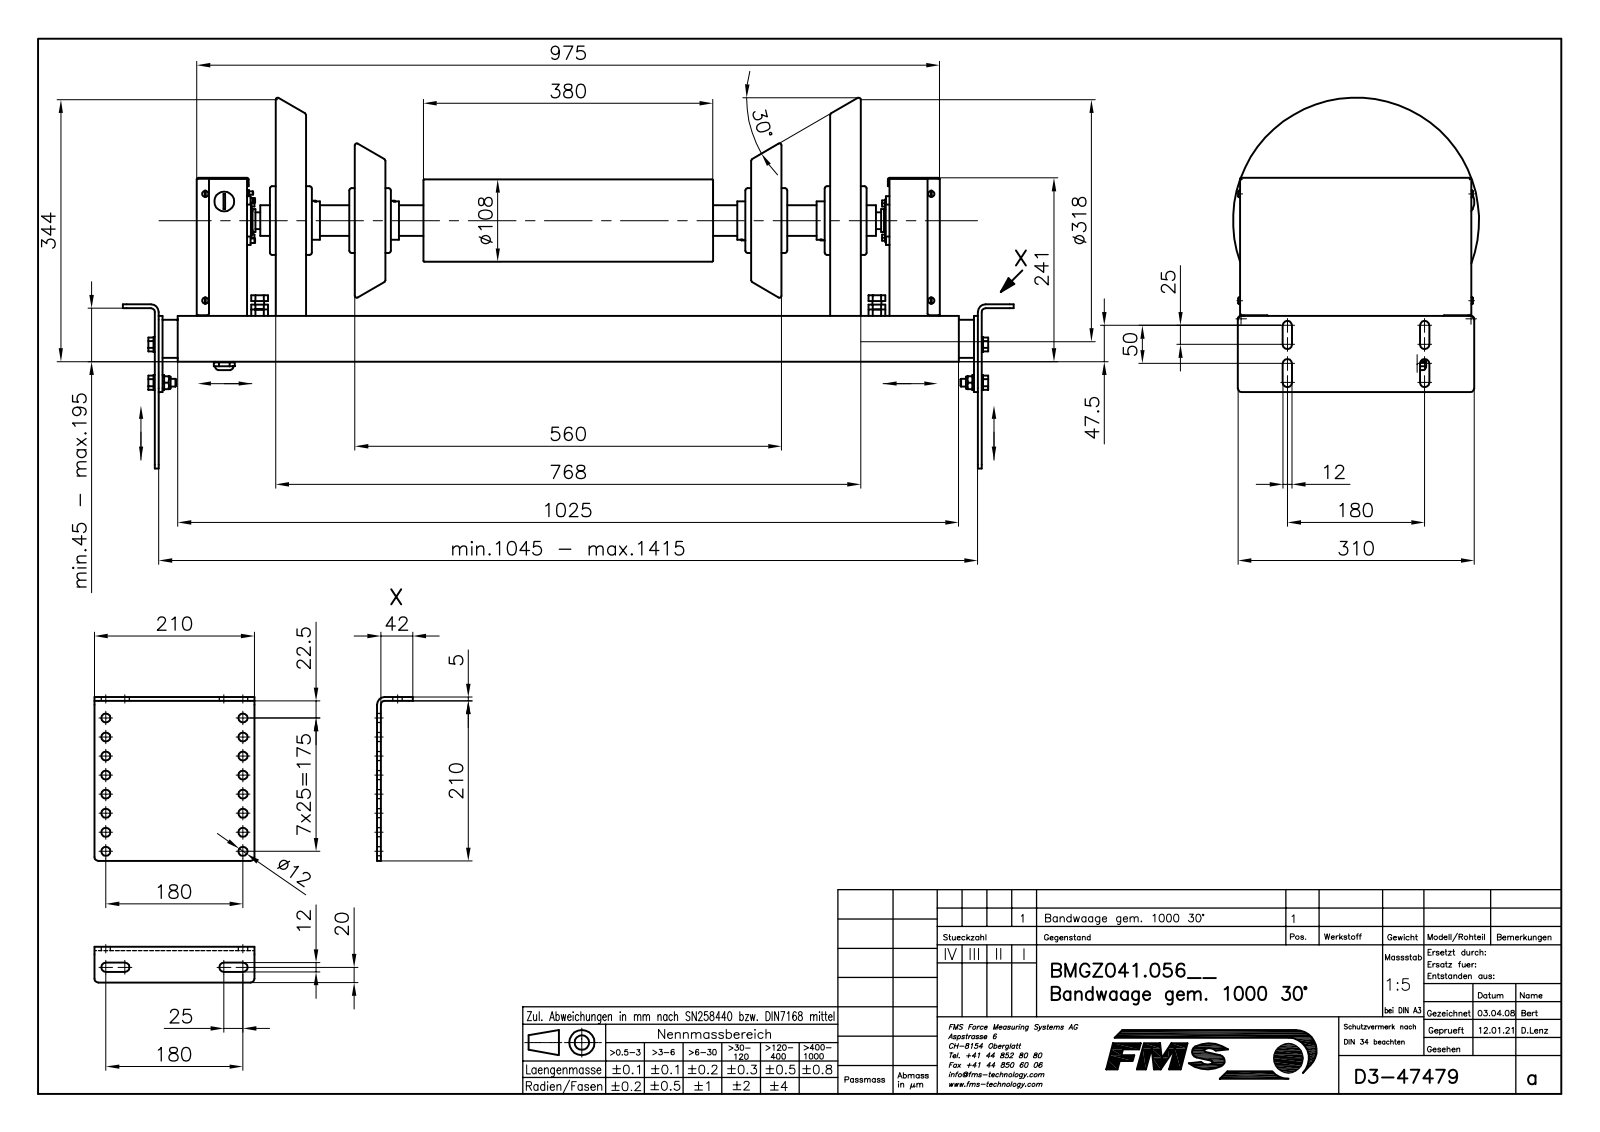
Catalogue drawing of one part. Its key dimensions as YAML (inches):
part_name: "B47479_STP; B50108; 6KT-SCHRAUBE_M12X30; ZYL_SCHR__M4X8 (+8 more)"
step_written_by: "Mechanical Desktop 2009 (CONFIG_CONTROL_DESIGN)"
units: inches
bodies: {solids: 179, faces: 2980, planar: 1435, cylindrical: 1070, other: 475}
overall_size: [46.024, 19.144, 12.698]
volume: 515.1
surface_area: 5971
round_holes:
  - {diameter: 0.472, count: 17}
  - {diameter: 0.197, count: 6}
  - {diameter: 0.138, count: 4}
  - {diameter: 0.193, count: 4}
  - {diameter: 0.252, count: 4}
  - {diameter: 0.272, count: 4}
  - {diameter: 0.342, count: 4}
  - {diameter: 0.344, count: 4}
  - {diameter: 0.394, count: 4}
  - {diameter: 0.413, count: 4}
  - {diameter: 0.42, count: 4}
  - {diameter: 0.583, count: 4}
round_bosses_or_shafts:
  - {diameter: 0.472, count: 11}
  - {diameter: 0.323, count: 8}
  - {diameter: 0.165, count: 8}
  - {diameter: 0.787, count: 6}
  - {diameter: 0.394, count: 6}
  - {diameter: 0.315, count: 6}
  - {diameter: 0.197, count: 5}
  - {diameter: 0.63, count: 4}
partial_cylinders:
  - {radius: 0.079, count: 34}
  - {radius: 0.039, count: 24}
  - {radius: 0.157, count: 16}
  - {radius: 0.197, count: 16}
  - {radius: 0.236, count: 12}
  - {radius: 0.138, count: 8}
  - {radius: 0.089, count: 6}
  - {radius: 0.02, count: 4}
face_to_face_distances: [0.157, 0.197, 0.039, 2.008, 10.63, 1.417, 2.205, 0.118, 1.969, 2.598]
hole_center_spacings: [0.984, 7.155, 1.969, 7.355, 2.953, 7.677, 3.937, 7.087]
